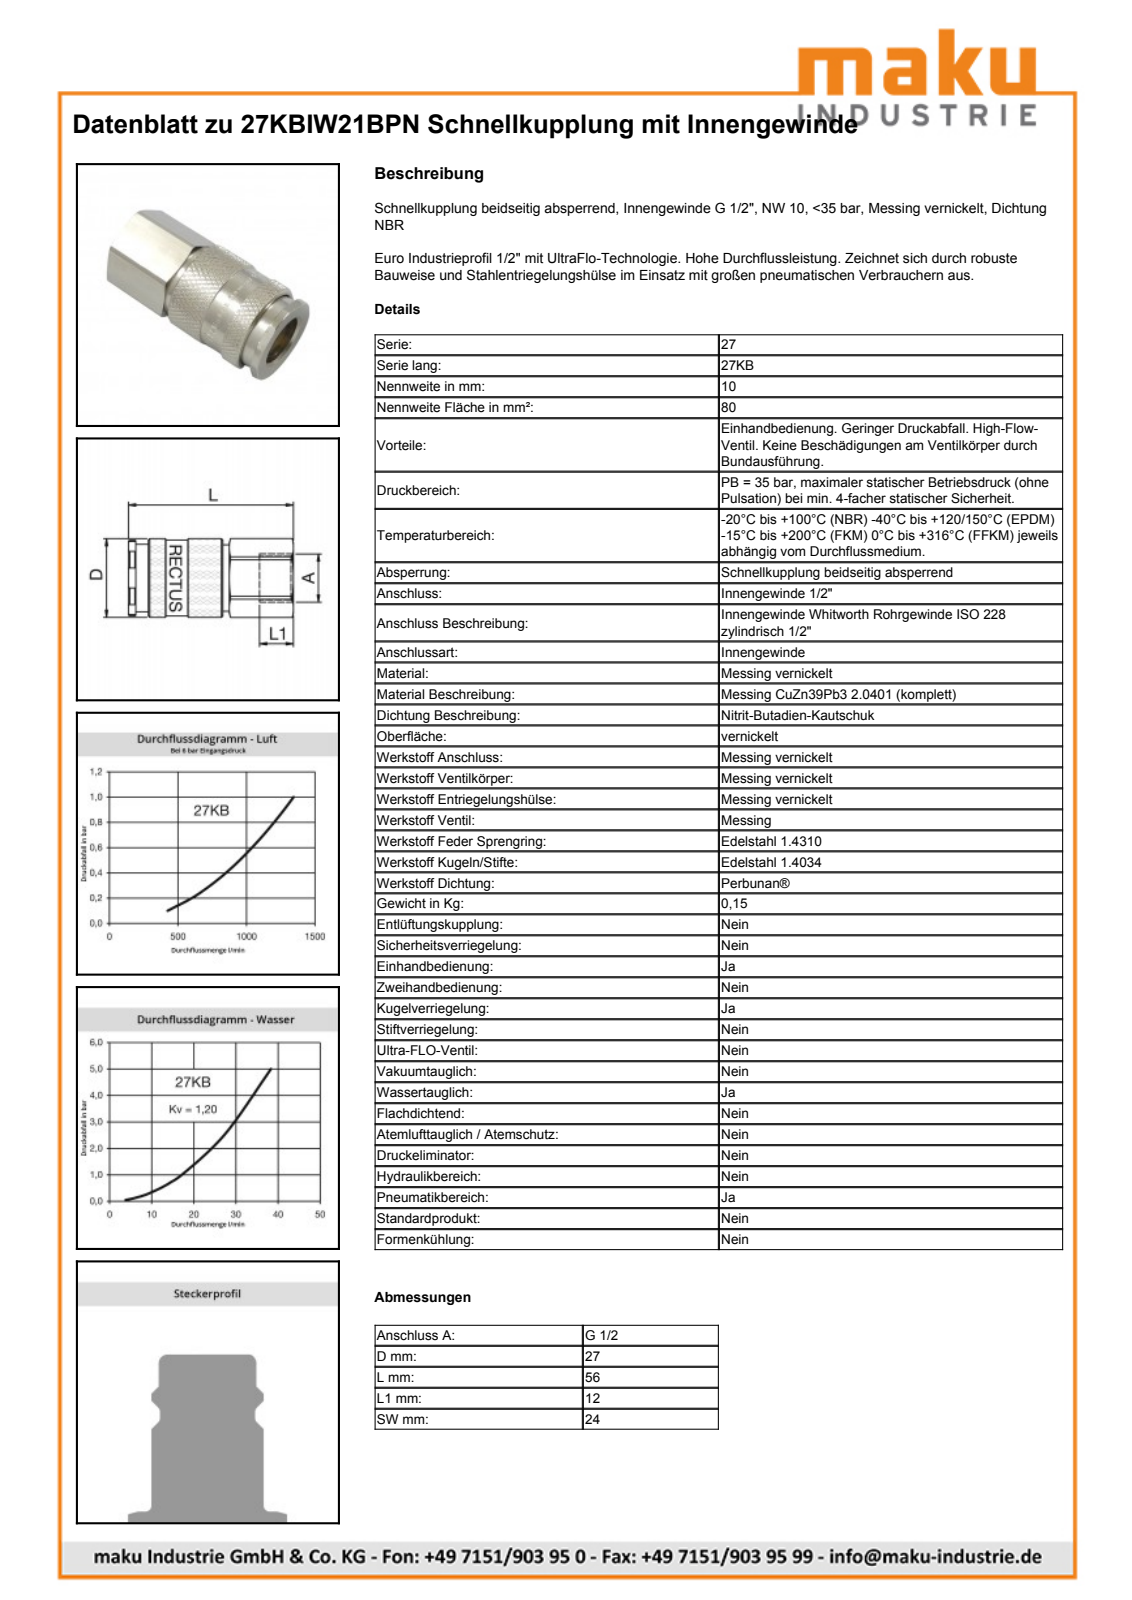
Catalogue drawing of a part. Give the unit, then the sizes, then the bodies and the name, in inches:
Units: inches
Overall size (bounding box): 2.222 × 1.069 × 1.069
Round holes (diameter × count): ⌀0.709 ×1, ⌀0.733 ×1, ⌀0.825 ×1, ⌀0.919 ×1, ⌀0.927 ×1
Round bosses / shafts (diameter × count): ⌀1.069 ×1, ⌀1.024 ×1, ⌀0.909 ×1, ⌀0.896 ×1, ⌀0.787 ×1
Partial cylindrical surfaces — rounded edges, fillets, slot ends (radius × count): R0.381 ×1, R0.39 ×1, R0.508 ×1, R0.533 ×1
Main face-to-face distances: 0.945, 0.946, 1.749, 1.272, 0.477, 2.222, 0.951, 0.474, 0.268, 1.004
Volume: 1.463 in³ · Surface area: 16.45 in²
Bodies: 2 solids, 652 faces (226 planar, 80 cylindrical, 346 other)
Part name (STEP PRODUCT): D106729
STEP written by: Autodesk Inventor 2013 (AUTOMOTIVE_DESIGN)
